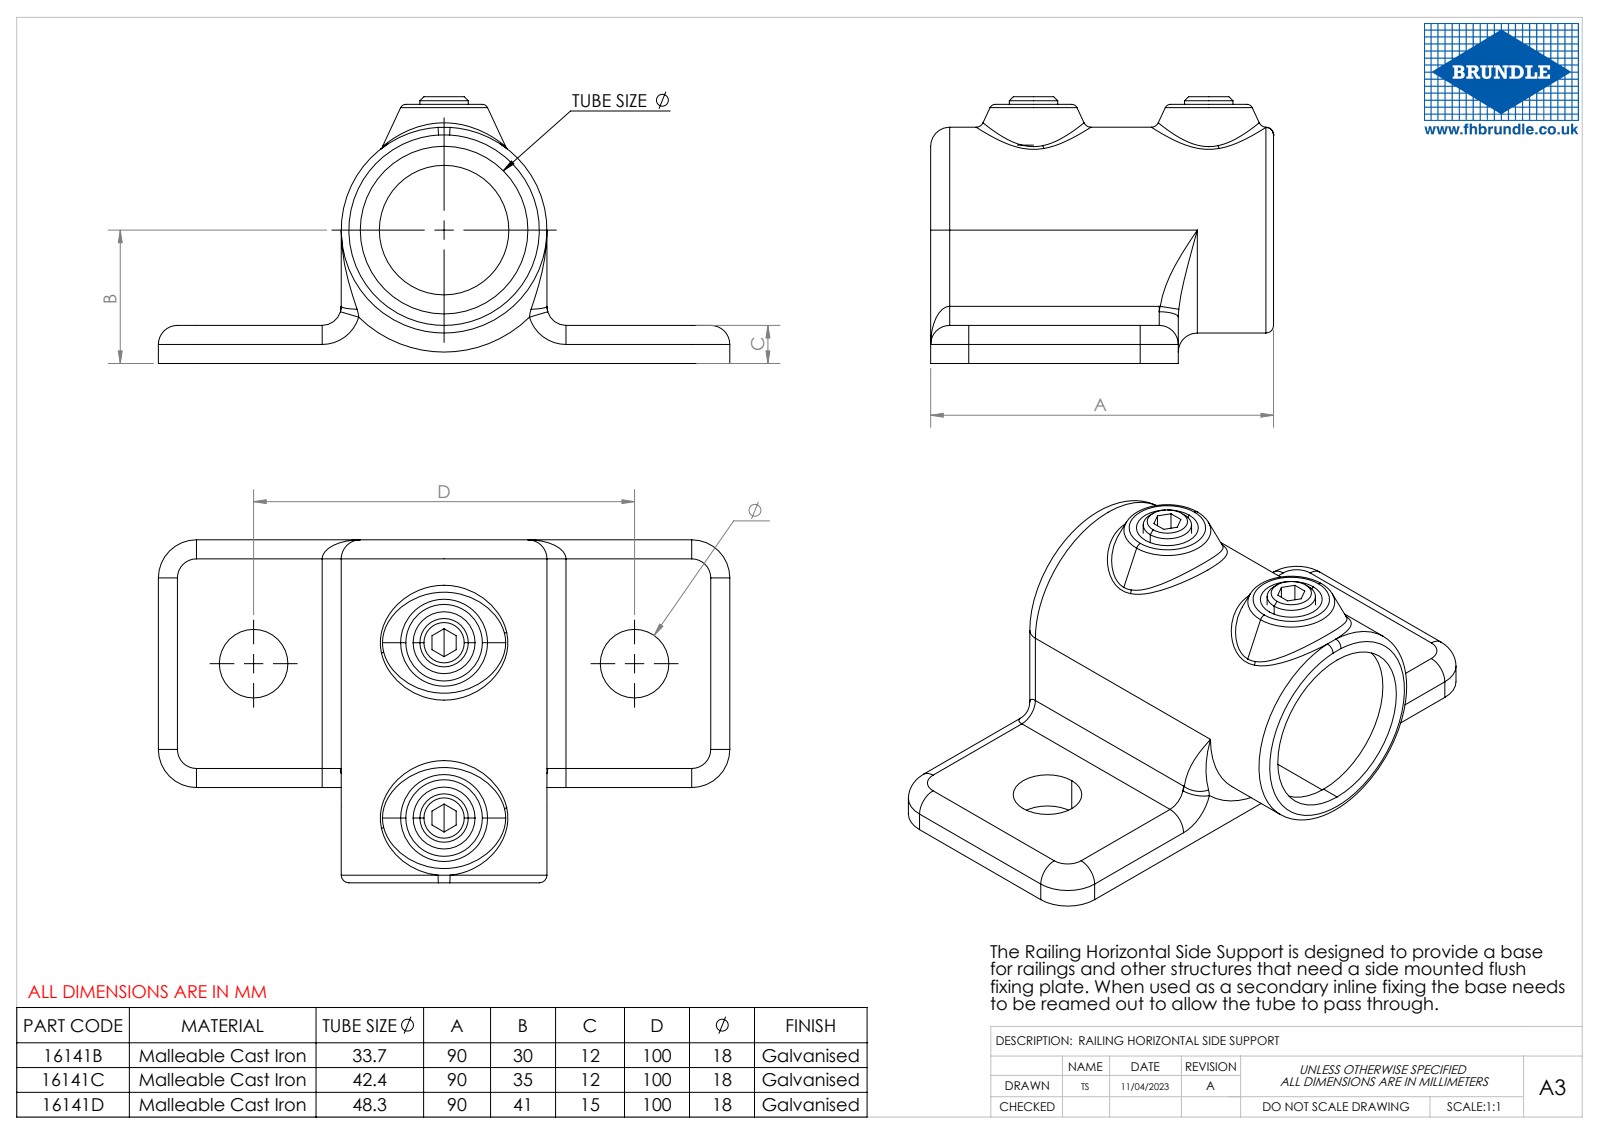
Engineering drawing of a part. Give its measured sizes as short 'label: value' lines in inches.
name: 16141D
written by: SolidWorks 2018 (CONFIG_CONTROL_DESIGN)
unit: in
bodies: 3 solids, 161 faces (0 planar, 0 cylindrical, 161 other)
size: 5.906 × 3.543 × 3.11
volume: 13.34 in³; area: 89.69 in²
